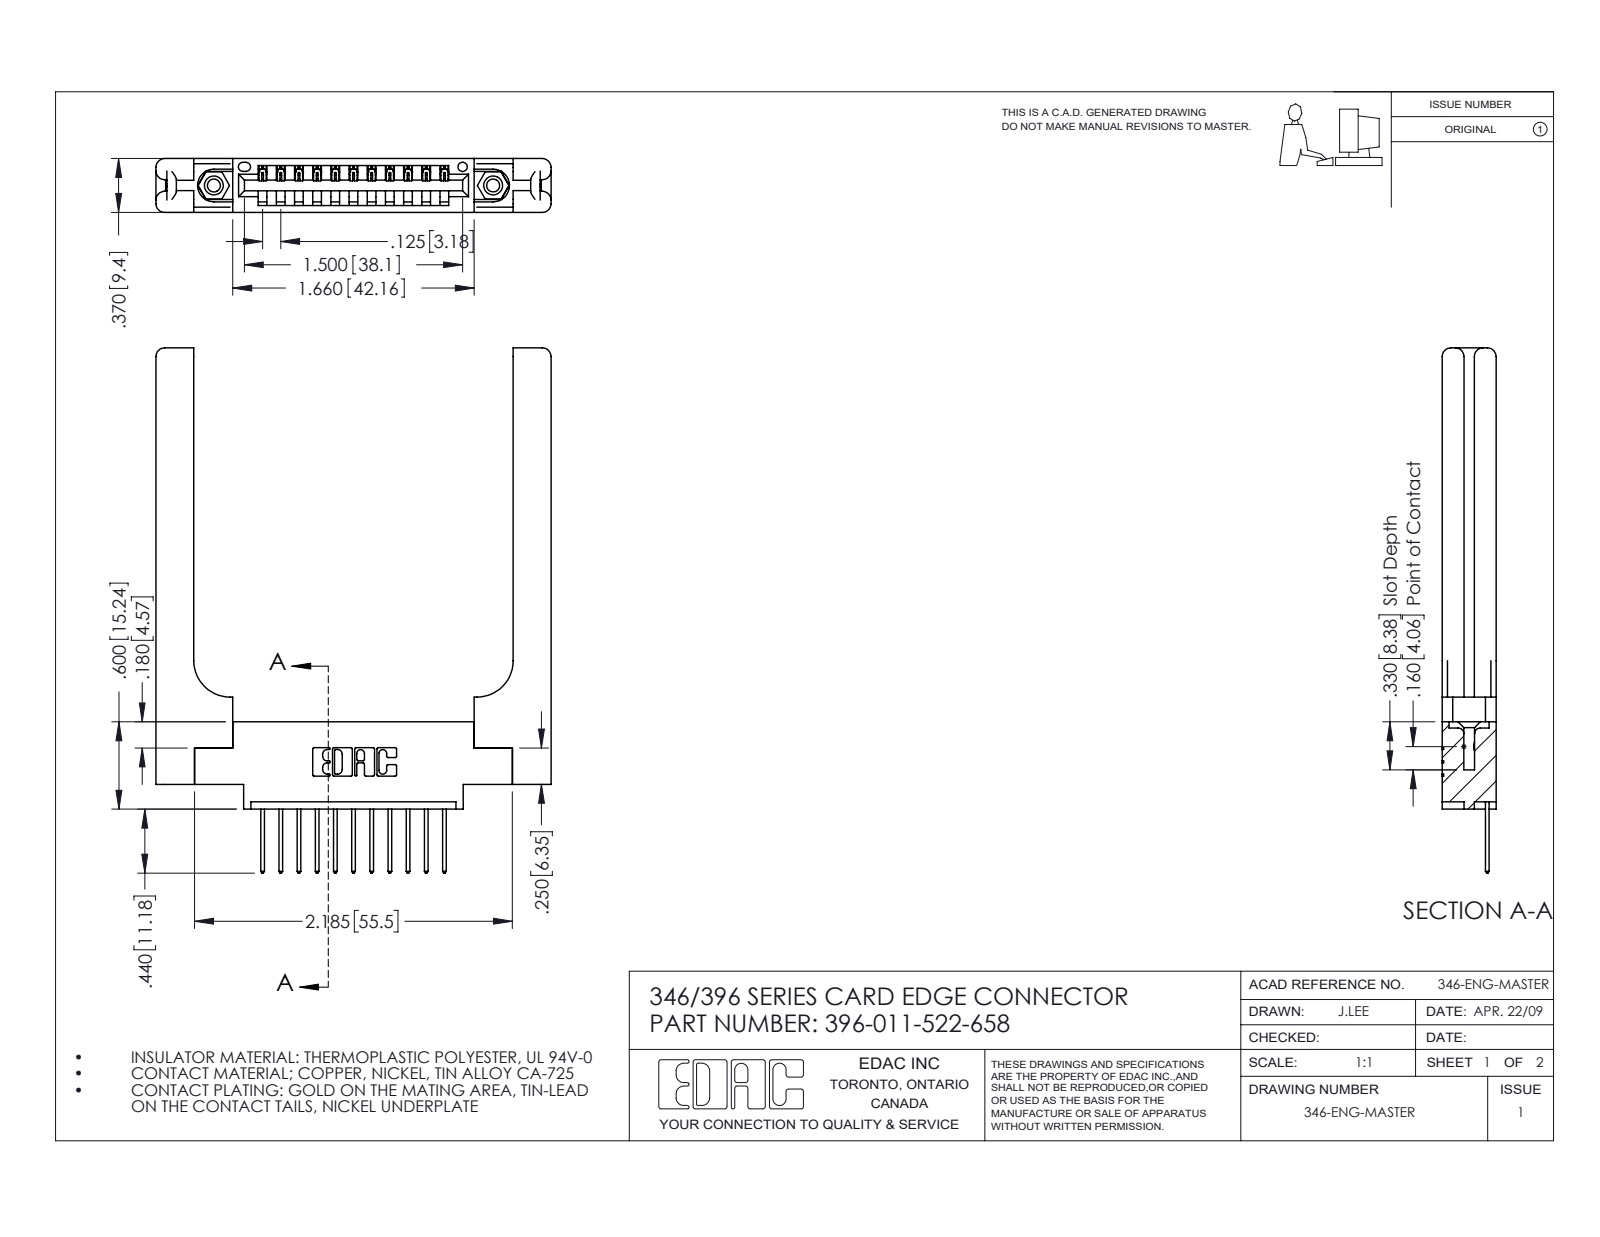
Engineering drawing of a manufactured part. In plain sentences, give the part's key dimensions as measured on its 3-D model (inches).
The part is named "346-220-058_345-220-058; 345-250-001_345-250-001-102; 396-011-522-658; 345-292-001_345-293-122 (+1 more)". Its 3-D file was written by "SolidWorks 2016 (CONFIG_CONTROL_DESIGN)". It is 16 solids with 1020 faces: 668 planar, 292 cylindrical and 60 other. Overall it measures 3.61 by 2.716 by 0.37 inches. Its volume is 0.839 cubic inches and its surface area 19.89 square inches. Round holes: 2 of diameter 0.089, 2 of diameter 0.125, 2 of diameter 0.156, 1 of diameter 0.064. Round bosses or shafts: 2 of diameter 0.155. Partial cylindrical surfaces (rounded edges, fillets, slot ends): 22 of radius 0.006, 22 of radius 0.01, 22 of radius 0.01, 16 of radius 0.06, 6 of radius 0.007, 6 of radius 0.031, 3 of radius 0.026, 2 of radius 0.03. The main face-to-face distances are 0.37, 0.15, 0.072, 0.148, 0.22, 0.048, 0.322, 0.102, 0.25, 0.173. The hole center spacings are 0.246, 1.715, 1.92.
